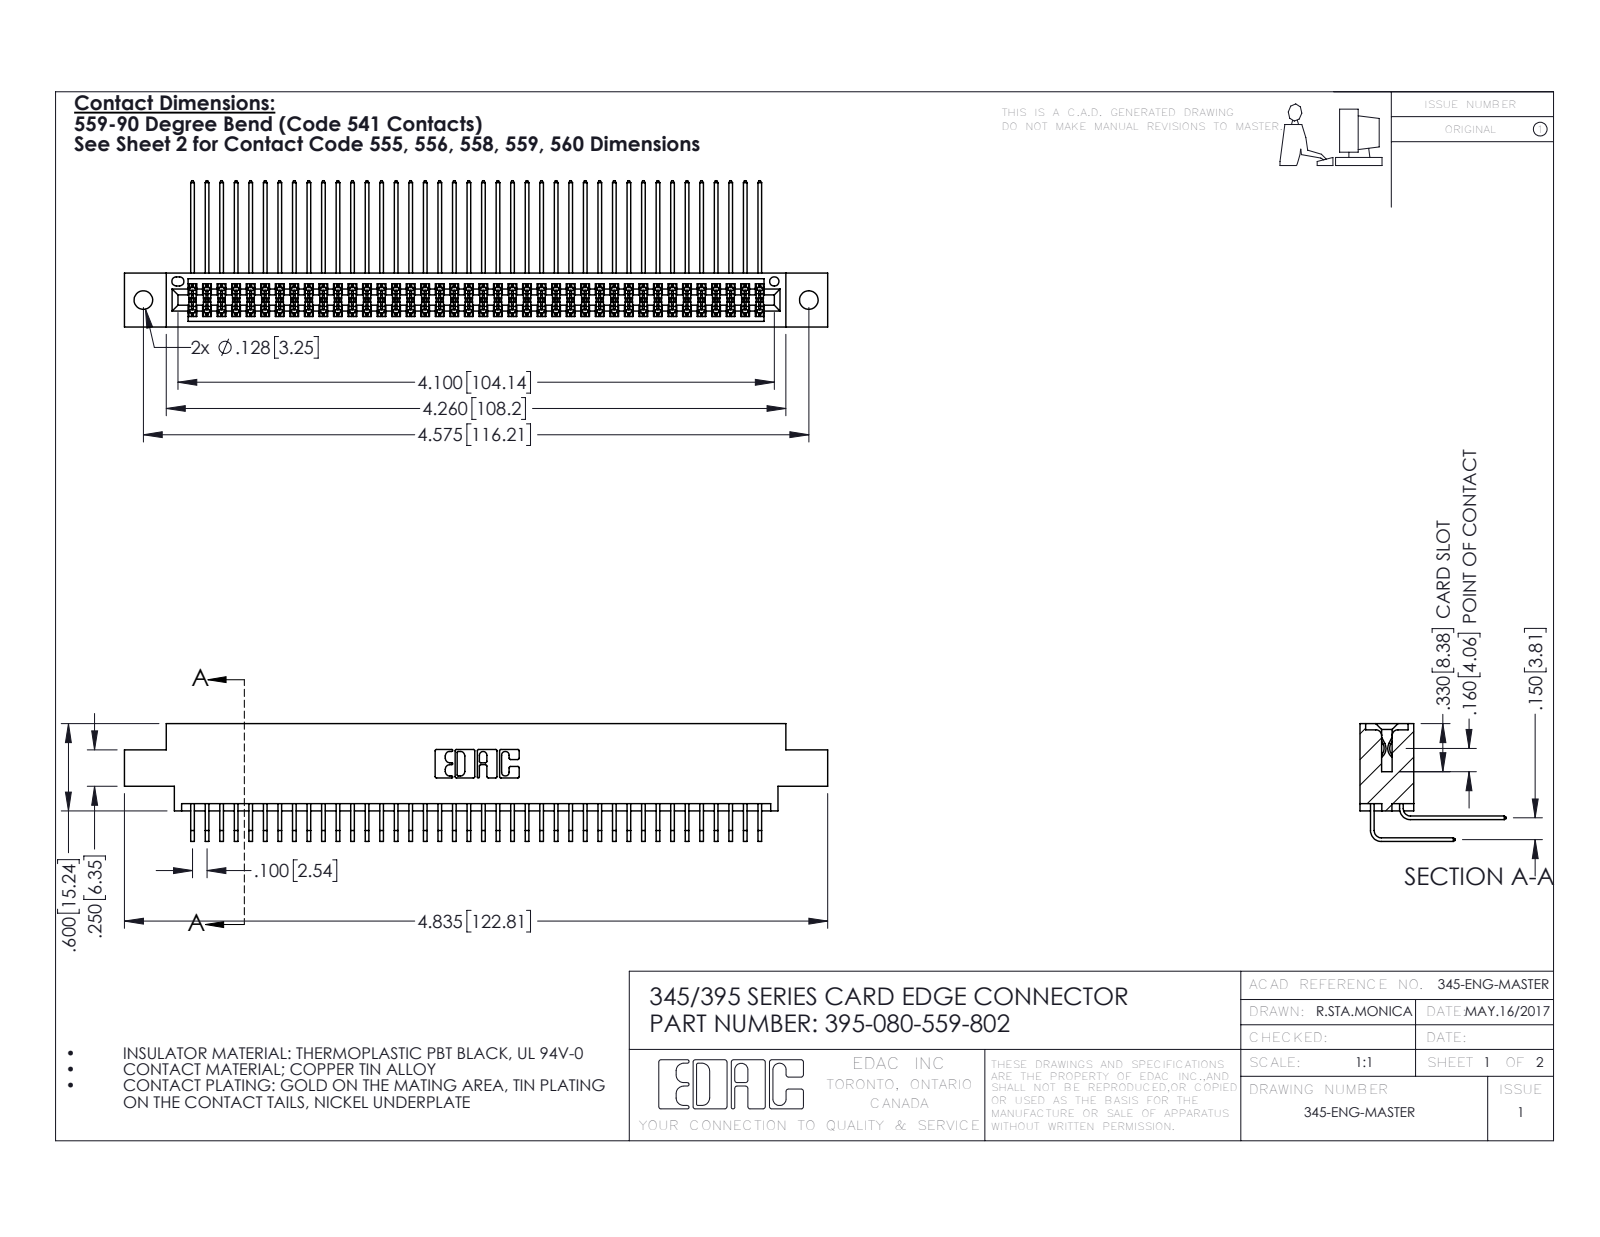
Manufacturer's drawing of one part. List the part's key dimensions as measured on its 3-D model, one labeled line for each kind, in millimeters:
Part name (STEP PRODUCT): 345 Part_0.170 Offset - 0.128 Dia; 345-292-001_559 Tail - 2; 395-080-559-802; 345-292-001_558 559 Tail - 1
STEP written by: SolidWorks 2016 (CONFIG_CONTROL_DESIGN)
Units: millimetres
Bodies: 81 solids, 4290 faces (2884 planar, 1406 cylindrical, 0 other)
Overall size (bounding box): 122.8 × 25.5 × 20.5
Volume: 12 200 mm³ · Surface area: 20 070 mm²
Round holes (diameter × count): ⌀3.3 ×2, ⌀1.6 ×1
Partial cylindrical surfaces — rounded edges, fillets, slot ends (radius × count): R0.2 ×121, R0.3 ×22, R0.2 ×6, R0.8 ×6, R0.7 ×3, R0.4 ×2, R0.5 ×2, R0.6 ×2
Main face-to-face distances: 1.8, 7.6, 9.4, 5.1, 2.5, 6.9, 0.6, 5.7, 4.4, 3.8
Hole centre spacings: 6.9, 110.2, 116.2
